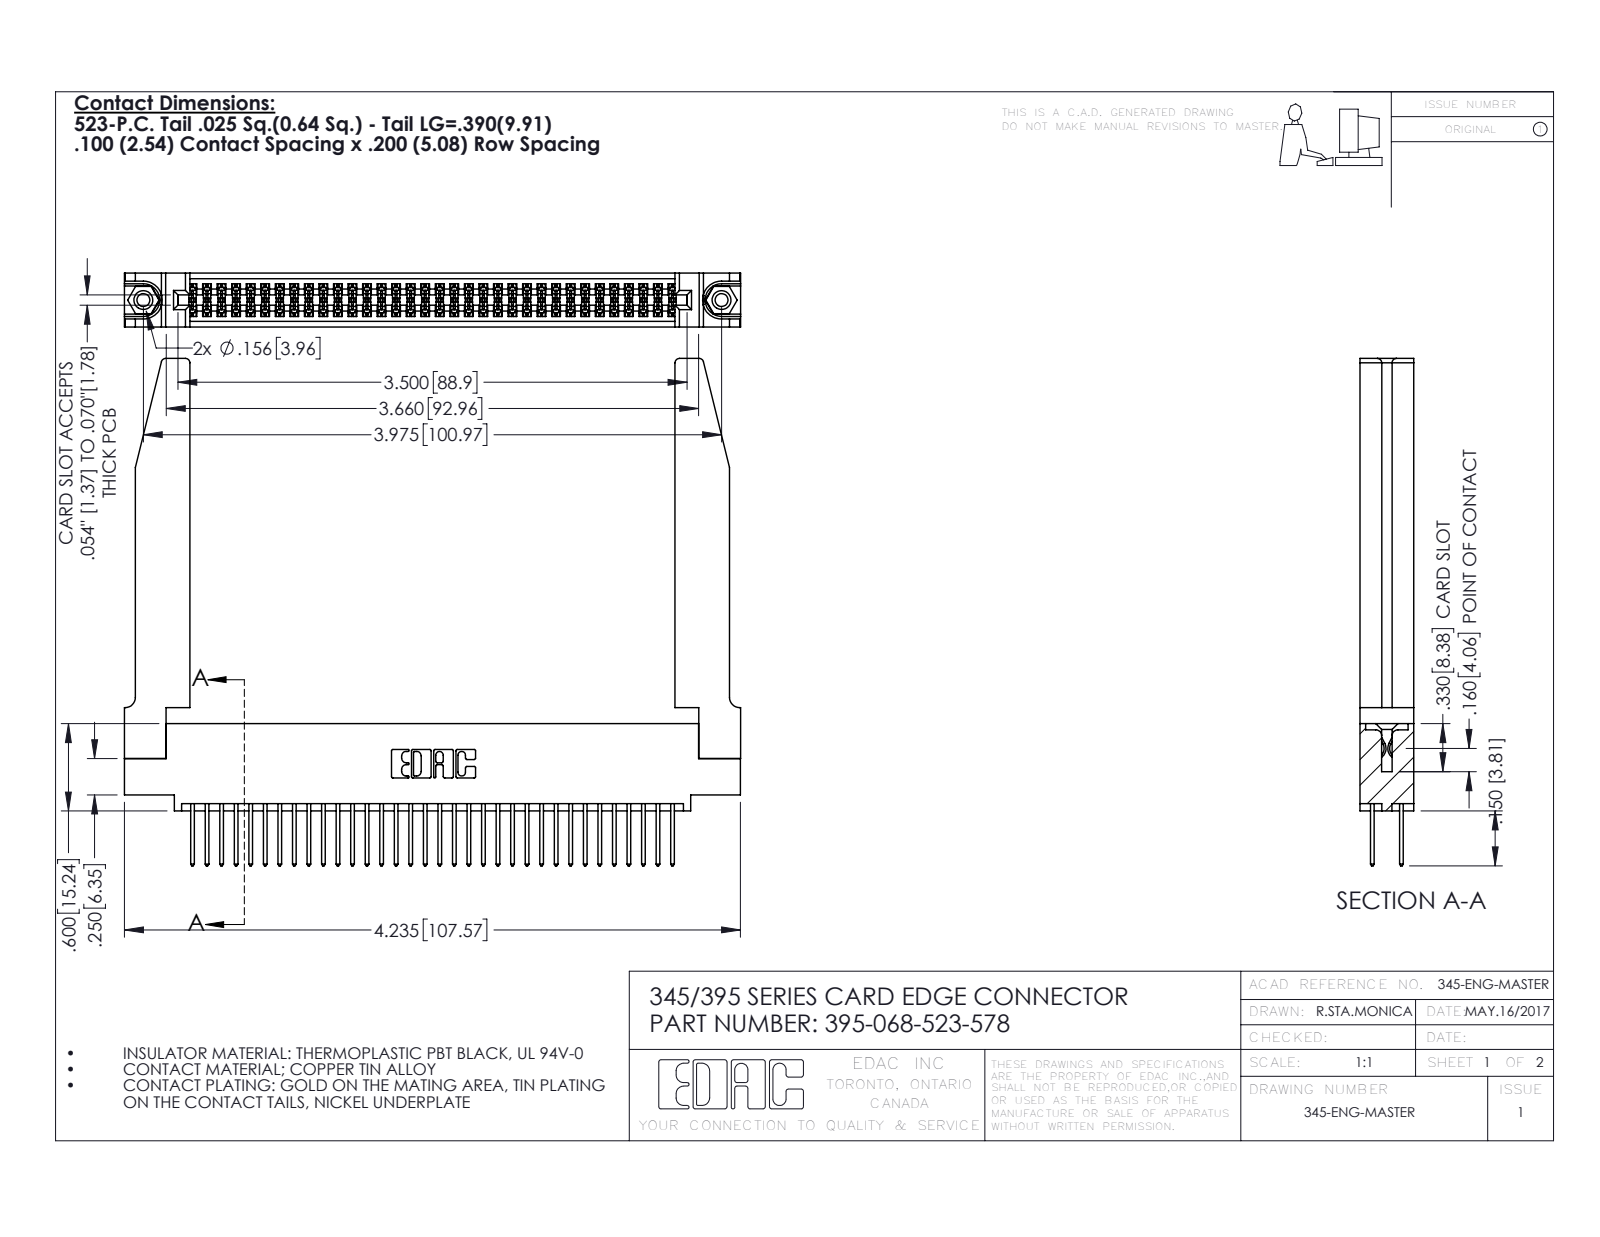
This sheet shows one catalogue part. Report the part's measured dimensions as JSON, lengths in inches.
{"part_name": "345-250-001_345-250-001-102; 345-220-078_345-220-078; 345 Part_0.110 Offset - 0.156 Dia-TH; 345-292-001_345-293-123 (+1 more)", "step_written_by": "SolidWorks 2016 (CONFIG_CONTROL_DESIGN)", "units": "inches", "bodies": {"solids": 73, "faces": 3764, "planar": 2470, "cylindrical": 1242, "other": 52}, "overall_size": [4.236, 3.487, 0.37], "volume_in3": 1.111, "surface_area_in2": 35.4, "round_holes": [[0.089, 2], [0.125, 2], [0.156, 2], [0.064, 1]], "round_bosses_or_shafts": [[0.155, 2]], "partial_cylinders_radius": [[0.006, 102], [0.01, 68], [0.01, 22], [0.03, 8], [0.007, 6], [0.031, 6], [0.026, 3], [0.014, 2]], "face_to_face_distances": [0.072, 0.37, 0.298, 0.2, 0.098, 0.272, 0.025, 0.225, 0.175, 0.15], "hole_center_spacings": [0.27, 3.74, 3.975]}
